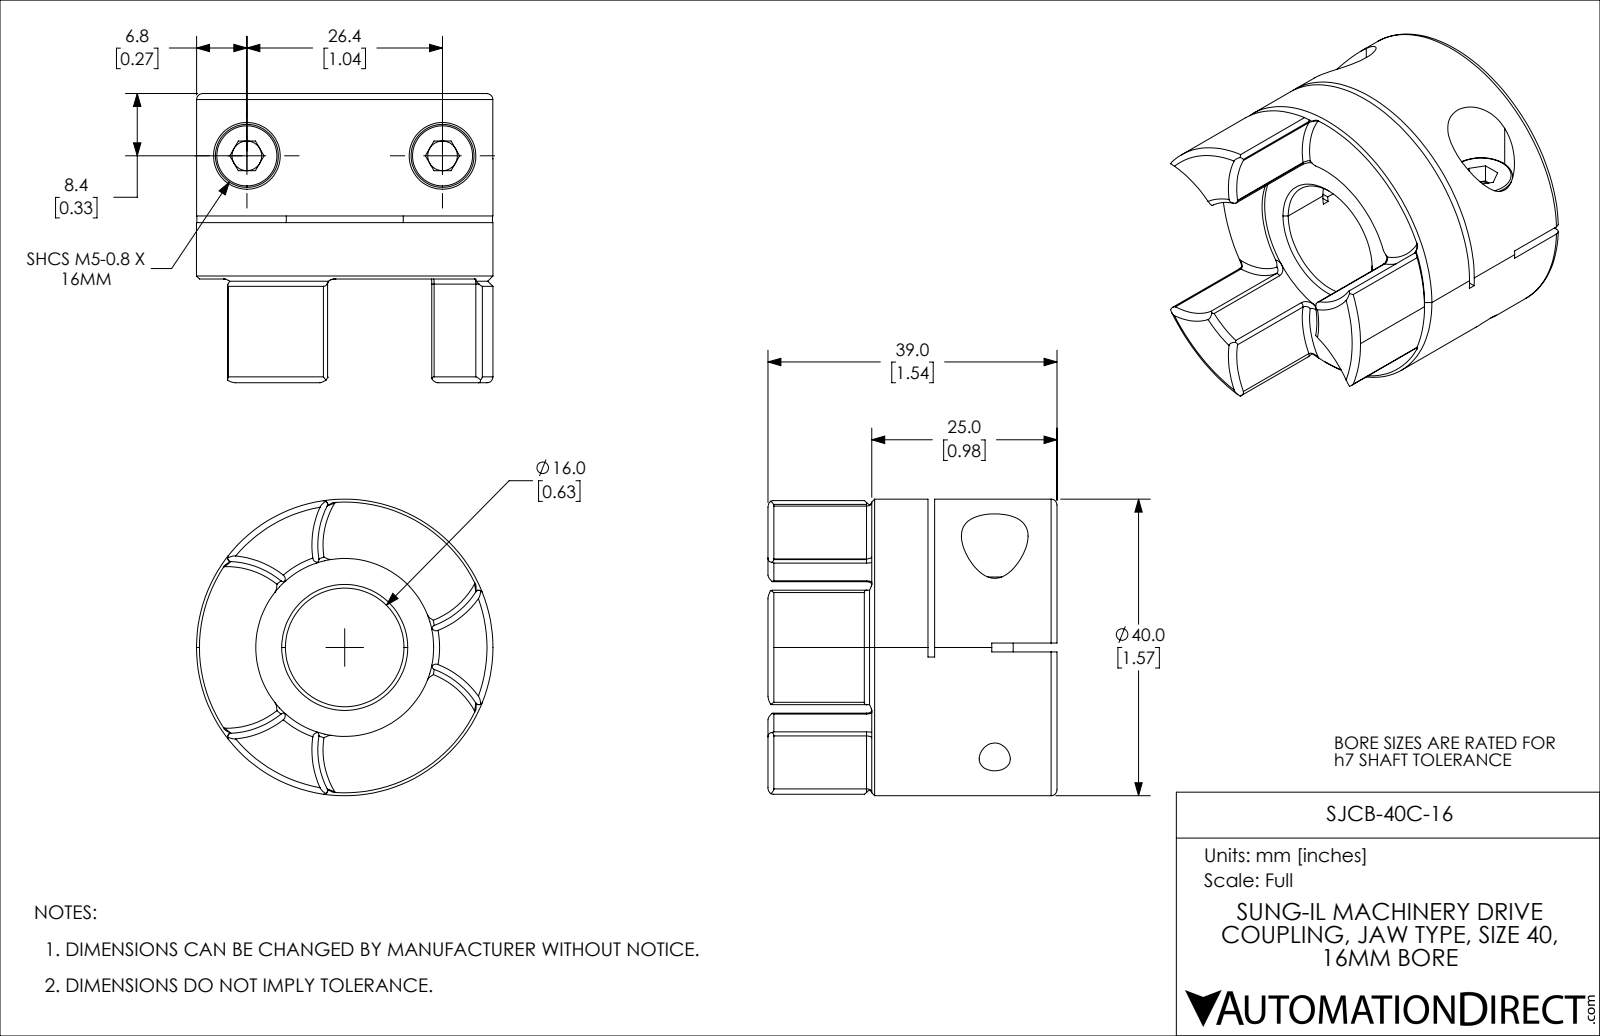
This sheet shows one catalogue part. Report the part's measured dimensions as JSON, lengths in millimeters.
{"part_name": "SJCB-40C-16", "step_written_by": "SolidWorks 2021 (CONFIG_CONTROL_DESIGN)", "units": "millimeters", "bodies": {"solids": 3, "faces": 184, "planar": 50, "cylindrical": 68, "other": 66}, "overall_size": [40, 40, 39], "volume_mm3": 27911, "surface_area_mm2": 11581, "round_holes": [[4, 2], [4.2, 2], [5.4, 2], [9, 2], [16, 1], [24, 1]], "round_bosses_or_shafts": [[8.5, 2], [5, 2], [40, 1]], "partial_cylinders_radius": [[0.5, 12], [11.6, 3], [40, 1]], "face_to_face_distances": [17.4, 0.9, 16.5, 7.6, 8.5, 25, 1.2, 0.5, 7.1, 8], "hole_center_spacings": [26.4]}
